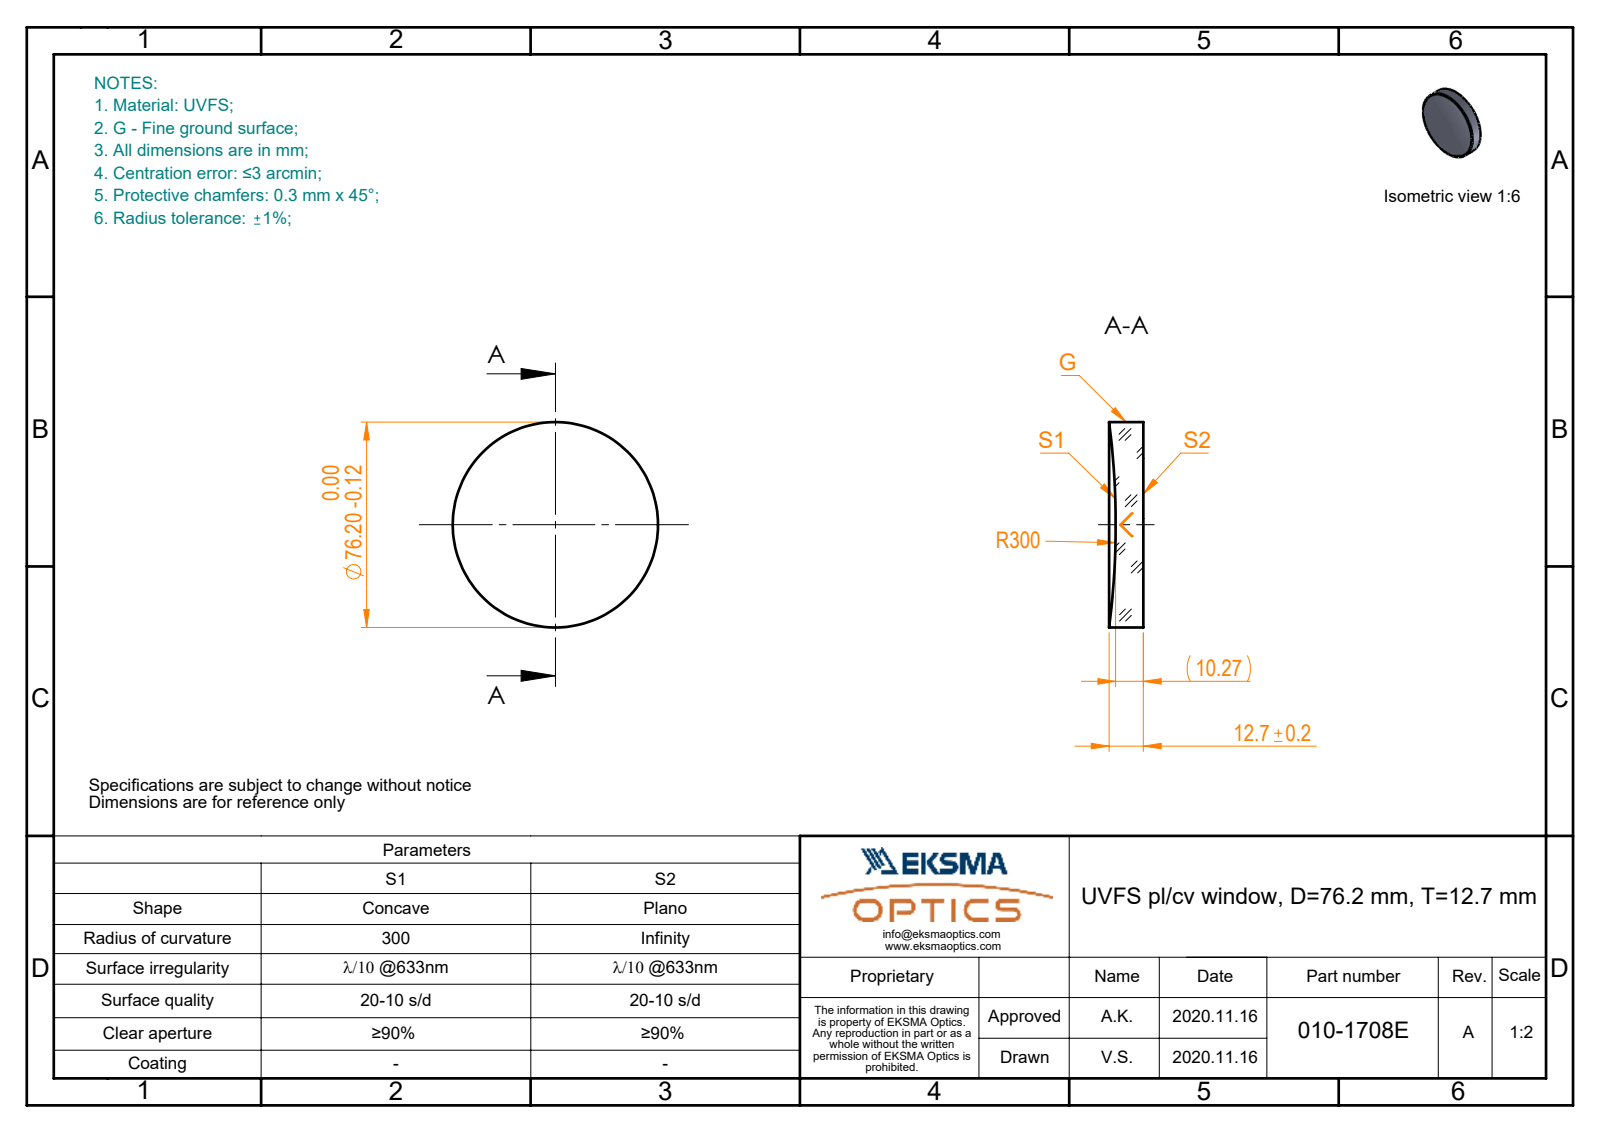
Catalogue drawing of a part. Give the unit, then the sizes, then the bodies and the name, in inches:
Units: inches
Overall size (bounding box): 3 × 3 × 0.5
Round bosses / shafts (diameter × count): ⌀3 ×1
Volume: 3.196 in³ · Surface area: 18.88 in²
Bodies: 1 solid, 5 faces (1 planar, 2 cylindrical, 2 other)
Part name (STEP PRODUCT): 010-1708E_UVFS_PCV_window
STEP written by: SolidWorks 2019 (CONFIG_CONTROL_DESIGN)
